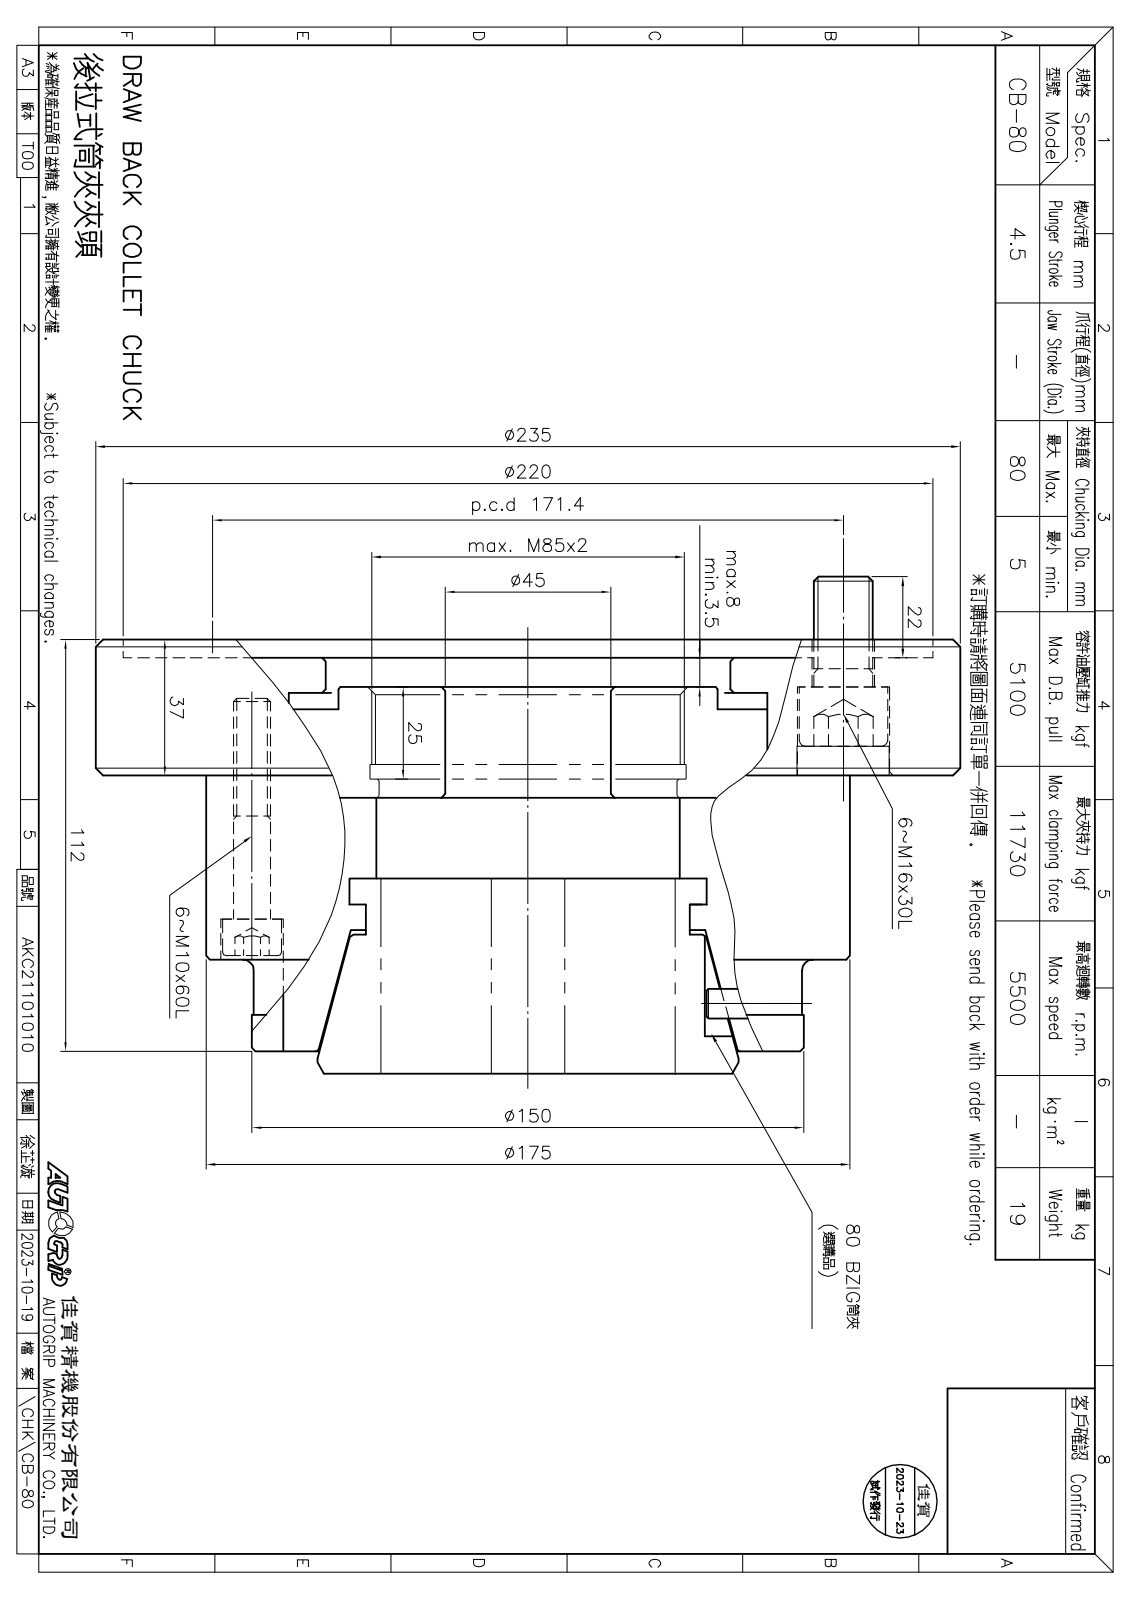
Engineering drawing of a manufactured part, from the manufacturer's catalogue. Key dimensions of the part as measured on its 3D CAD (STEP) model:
Part name (STEP PRODUCT): CL-80-09000; CF-CB-80; CF-CB-80-02000; CF-RG-80R (+4 more)
STEP written by: SolidWorks 2020 (CONFIG_CONTROL_DESIGN)
Units: millimetres
Bodies: 19 solids, 713 faces (301 planar, 220 cylindrical, 192 other)
Overall size (bounding box): 235 × 235 × 135
Volume: 2 424 000 mm³ · Surface area: 384 768 mm²
Round holes (diameter × count): ⌀8.5 ×15, ⌀17 ×15, ⌀11 ×6, ⌀25 ×6, ⌀6.8 ×3, ⌀80 ×1, ⌀81 ×1, ⌀82 ×1, ⌀86 ×1, ⌀90 ×1, ⌀97 ×1, ⌀110 ×1
Round bosses / shafts (diameter × count): ⌀16 ×15, ⌀10 ×9, ⌀24 ×6, ⌀8 ×3, ⌀235 ×1, ⌀114.5 ×1, ⌀103 ×1, ⌀95 ×1
Partial cylindrical surfaces — rounded edges, fillets, slot ends (radius × count): R4 ×3, R74.5 ×1, R75 ×1
Main face-to-face distances: 28, 32, 4, 14, 8, 46, 74, 79, 33, 99
Hole centre spacings: 42.86, 75, 85.7, 113.88, 155.25, 34.19, 42.26, 45.75
